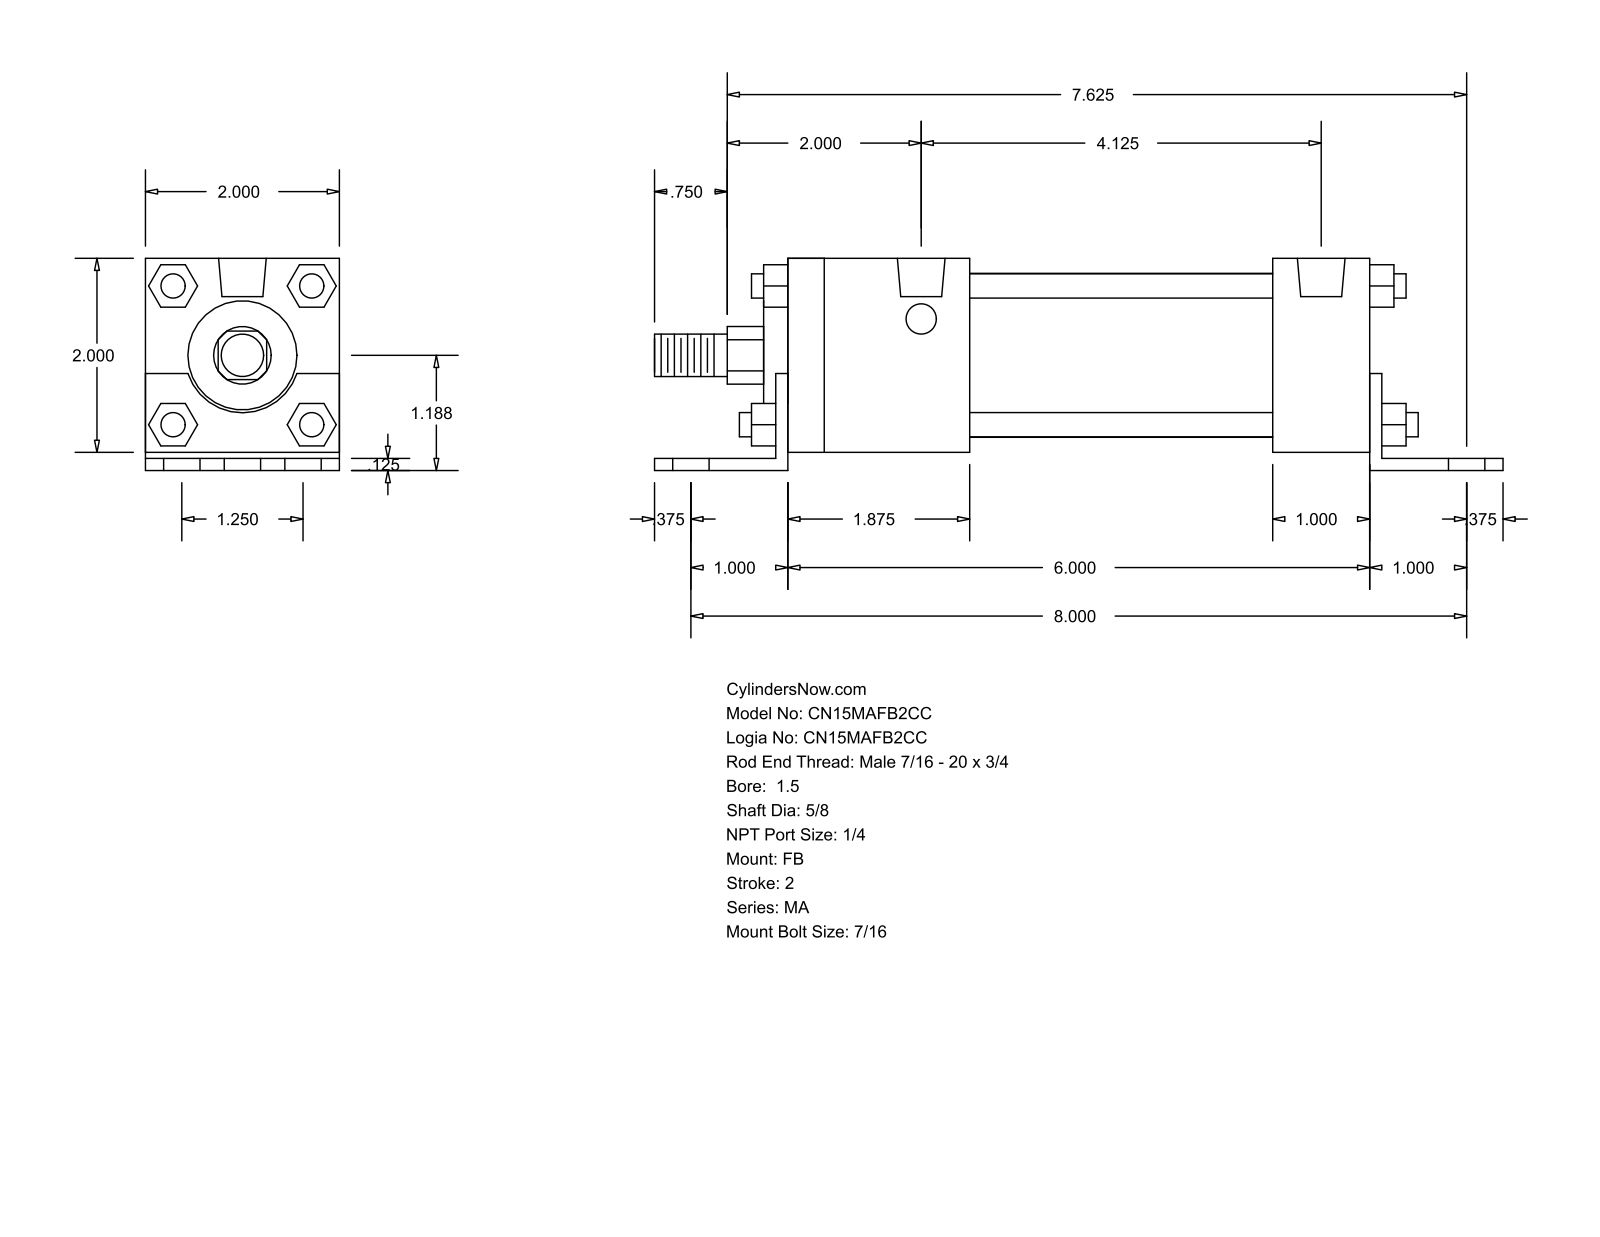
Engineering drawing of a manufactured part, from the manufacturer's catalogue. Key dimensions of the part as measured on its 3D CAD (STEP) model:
Part name (STEP PRODUCT): MA_FB__0150_0.625
STEP written by: GSSL Pune (CONFIG_CONTROL_DESIGN)
Units: millimetres
Bodies: 0 solids, 140 faces (105 planar, 35 cylindrical, 0 other)
Overall size (bounding box): 222.25 × 55.56 × 50.8
Round holes (diameter × count): ⌀11.11 ×6, ⌀7.94 ×4, ⌀12.49 ×2
Round bosses / shafts (diameter × count): ⌀6.35 ×4, ⌀42.93 ×1, ⌀28.57 ×1, ⌀15.88 ×1, ⌀11.11 ×1
Partial cylindrical surfaces — rounded edges, fillets, slot ends (radius × count): R7.54 ×1, R15.05 ×1
Main face-to-face distances: 50.8, 3.17, 4.76, 55.56, 1.59, 52.39, 25.4, 158.75, 6.35, 3.18
Hole centre spacings: 15.88, 203.83, 203.21, 31.76, 41.29, 62.38, 104.77, 143.76
